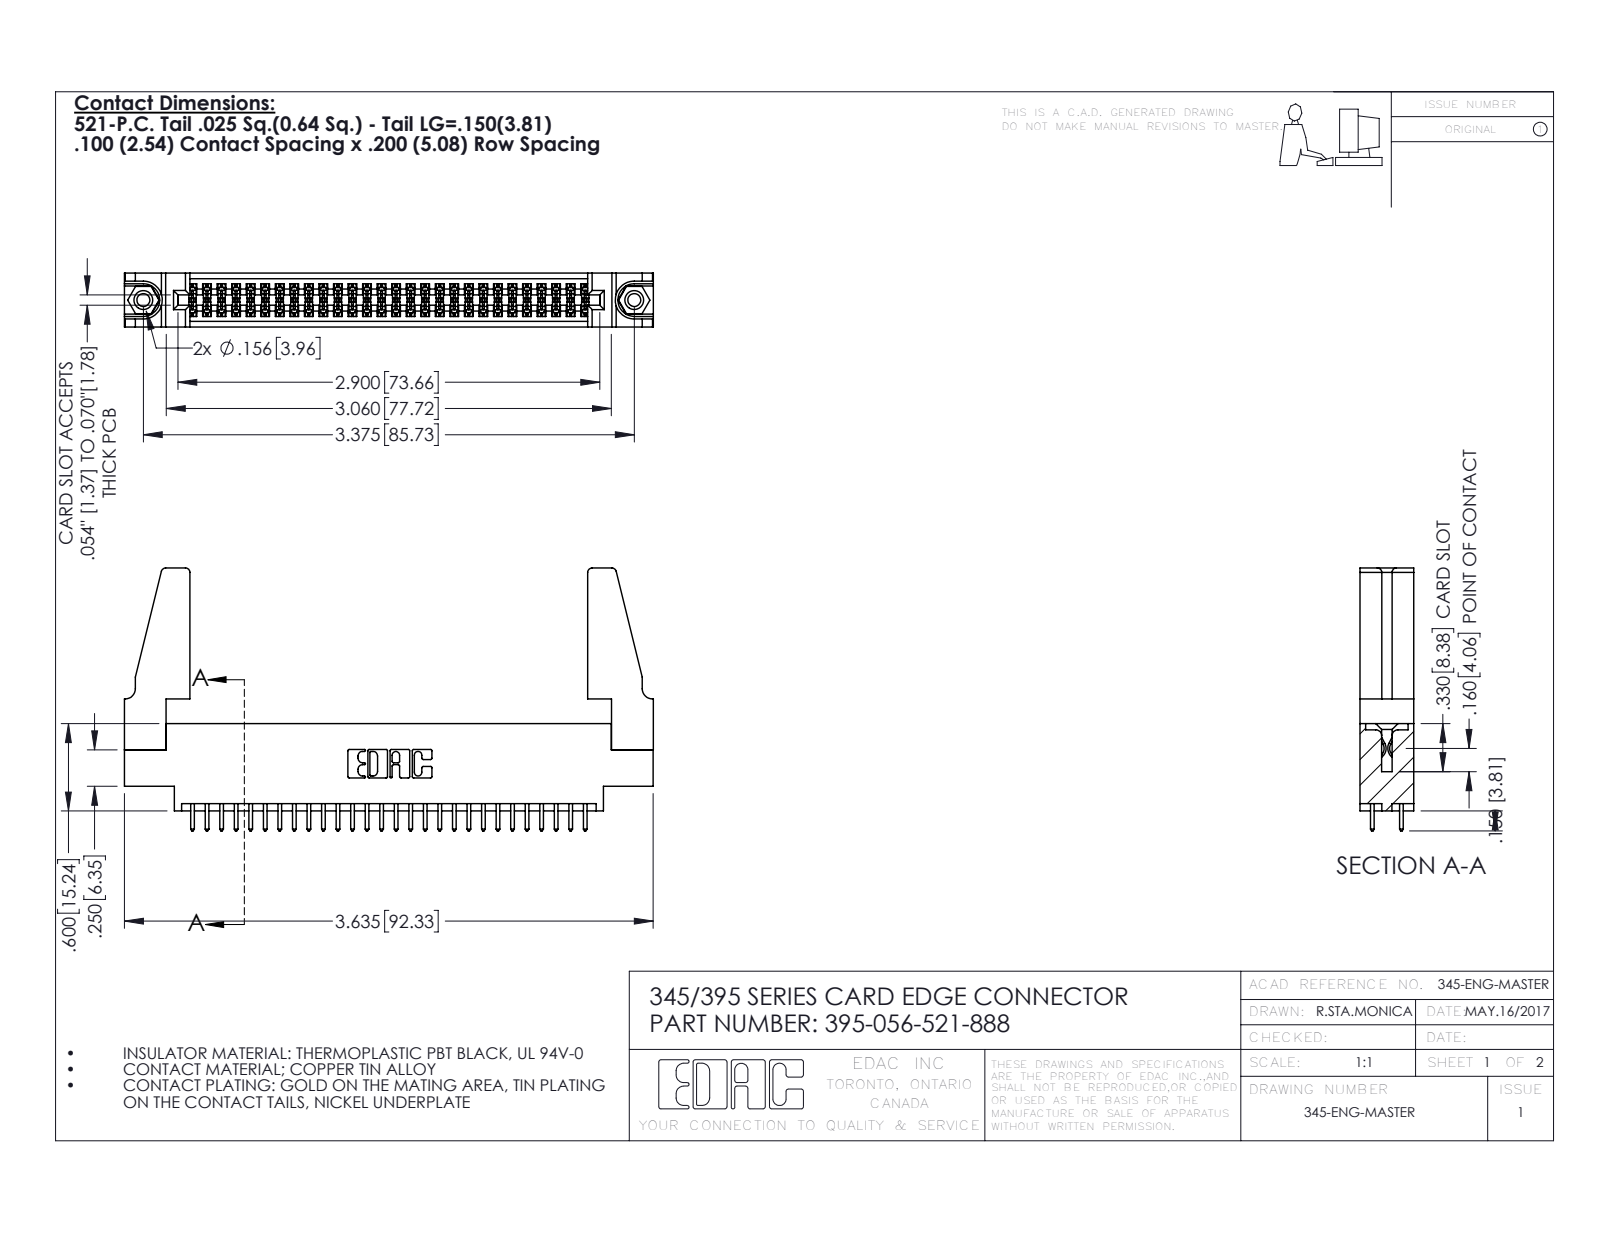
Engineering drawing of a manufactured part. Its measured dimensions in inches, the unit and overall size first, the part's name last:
Units: inches
Overall size (bounding box): 3.636 × 1.807 × 0.37
Round holes (diameter × count): ⌀0.089 ×2, ⌀0.125 ×2, ⌀0.156 ×2, ⌀0.064 ×1
Round bosses / shafts (diameter × count): ⌀0.155 ×2
Partial cylindrical surfaces — rounded edges, fillets, slot ends (radius × count): R0.006 ×84, R0.01 ×56, R0.01 ×22, R0.03 ×8, R0.007 ×6, R0.031 ×6, R0.026 ×3, R0.014 ×2
Main face-to-face distances: 0.072, 0.37, 0.298, 0.098, 0.272, 0.025, 0.2, 0.225, 0.175, 0.149
Hole centre spacings: 0.27, 3.14, 3.375
Volume: 0.73 in³ · Surface area: 24.36 in²
Bodies: 61 solids, 3054 faces (2004 planar, 1034 cylindrical, 16 other)
Part name (STEP PRODUCT): 345-250-001_345-250-001-102; 345-220-078_345-220-088; 395-056-521-888; 345 Part_0.170 Offset - 0.156 Dia-TH (+1 more)
STEP written by: SolidWorks 2016 (CONFIG_CONTROL_DESIGN)
